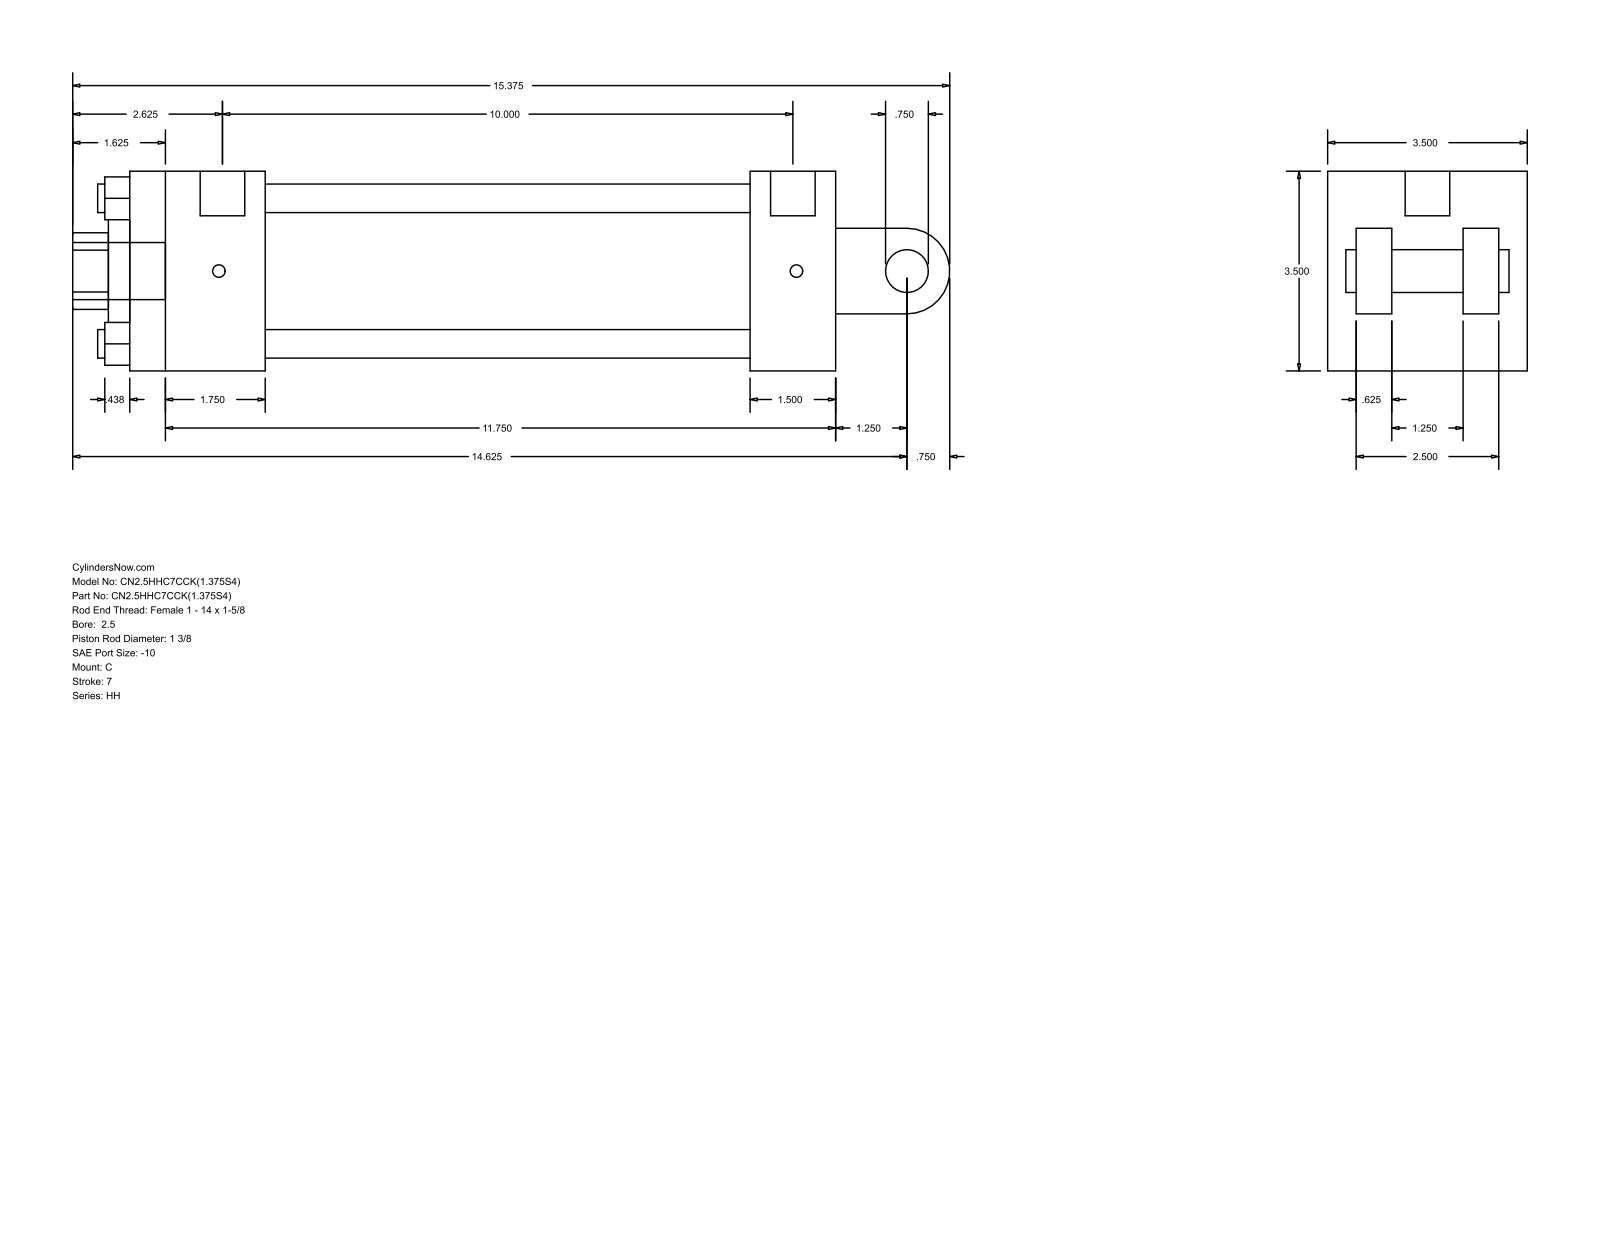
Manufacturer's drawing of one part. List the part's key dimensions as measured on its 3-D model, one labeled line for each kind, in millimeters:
Part name (STEP PRODUCT): HH_C__0250_1.375
STEP written by: GSSL Pune (CONFIG_CONTROL_DESIGN)
Units: millimetres
Bodies: 0 solids, 99 faces (70 planar, 29 cylindrical, 0 other)
Overall size (bounding box): 390.52 × 88.9 × 88.9
Round holes (diameter × count): ⌀12.7 ×4, ⌀5.56 ×2, ⌀19.84 ×1, ⌀34.92 ×1, ⌀50.8 ×1, ⌀73.03 ×1
Round bosses / shafts (diameter × count): ⌀5.56 ×2, ⌀25.4 ×1, ⌀19.84 ×1, ⌀19.05 ×1
Partial cylindrical surfaces — rounded edges, fillets, slot ends (radius × count): R17.06 ×1, R19.05 ×1
Main face-to-face distances: 88.9, 314.33, 63.5, 15.87, 12.7, 276.22, 38.11, 60.32, 215.9, 254.01
Hole centre spacings: 45.79, 64.76, 91.58, 1.58
